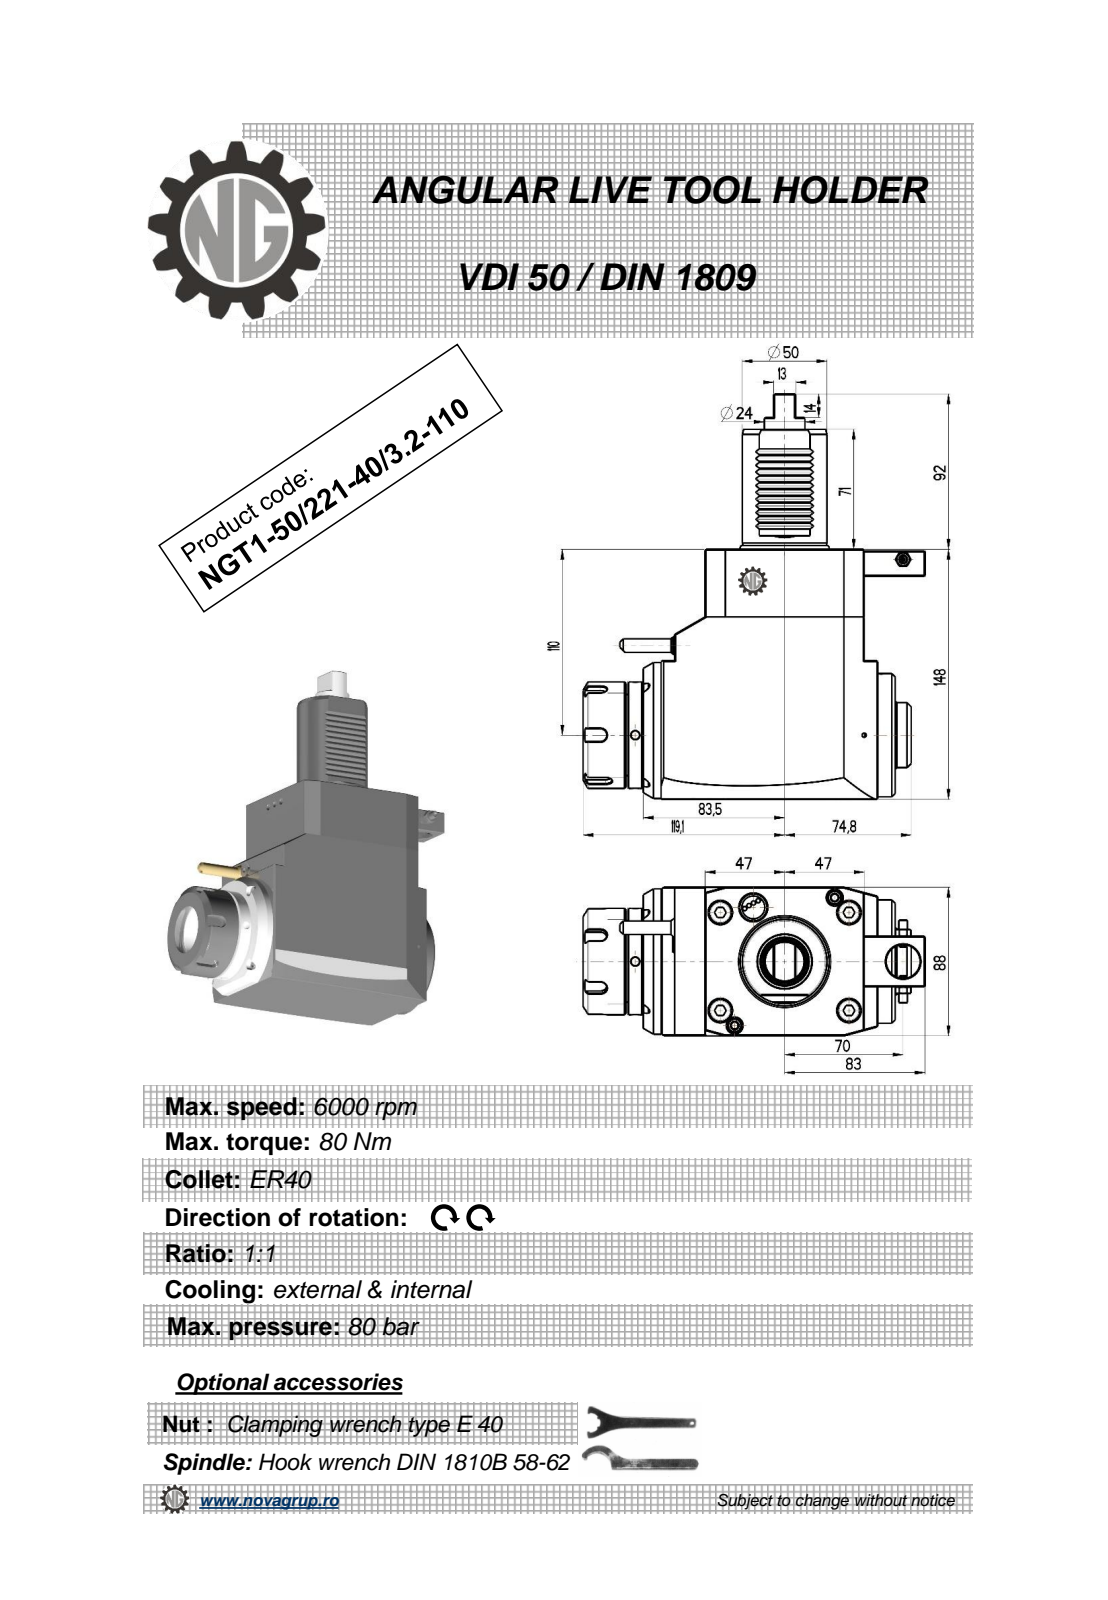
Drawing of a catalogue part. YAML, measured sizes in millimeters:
part_name: "NGT1_50_221_40_3_2_110"
step_written_by: "PRO/ENGINEER BY PARAMETRIC TECHNOLOGY CORPORATION, 2010280 (CONFIG_CONTROL_DESIGN)"
units: millimeters
bodies: {solids: 1, faces: 424, planar: 207, cylindrical: 98, other: 119}
overall_size: [240, 202.1, 88]
volume: 1847000
surface_area: 115937
round_holes:
  - {diameter: 5, count: 3}
  - {diameter: 3, count: 1}
  - {diameter: 4.5, count: 1}
  - {diameter: 9.5, count: 1}
  - {diameter: 20, count: 1}
  - {diameter: 33.5, count: 1}
round_bosses_or_shafts:
  - {diameter: 86, count: 1}
  - {diameter: 73, count: 1}
  - {diameter: 63, count: 1}
  - {diameter: 51, count: 1}
  - {diameter: 50, count: 1}
  - {diameter: 40, count: 1}
  - {diameter: 38.5, count: 1}
  - {diameter: 24, count: 1}
partial_cylinders:
  - {radius: 0.26, count: 12}
  - {radius: 0.3, count: 12}
  - {radius: 0.2, count: 6}
  - {radius: 3.75, count: 5}
  - {radius: 0.8, count: 2}
face_to_face_distances: [88, 148, 8, 94, 36.5, 130.5, 120, 148.8, 112.3, 18.3]
hole_center_spacings: [52.46, 56.65, 101.5, 158.25]
